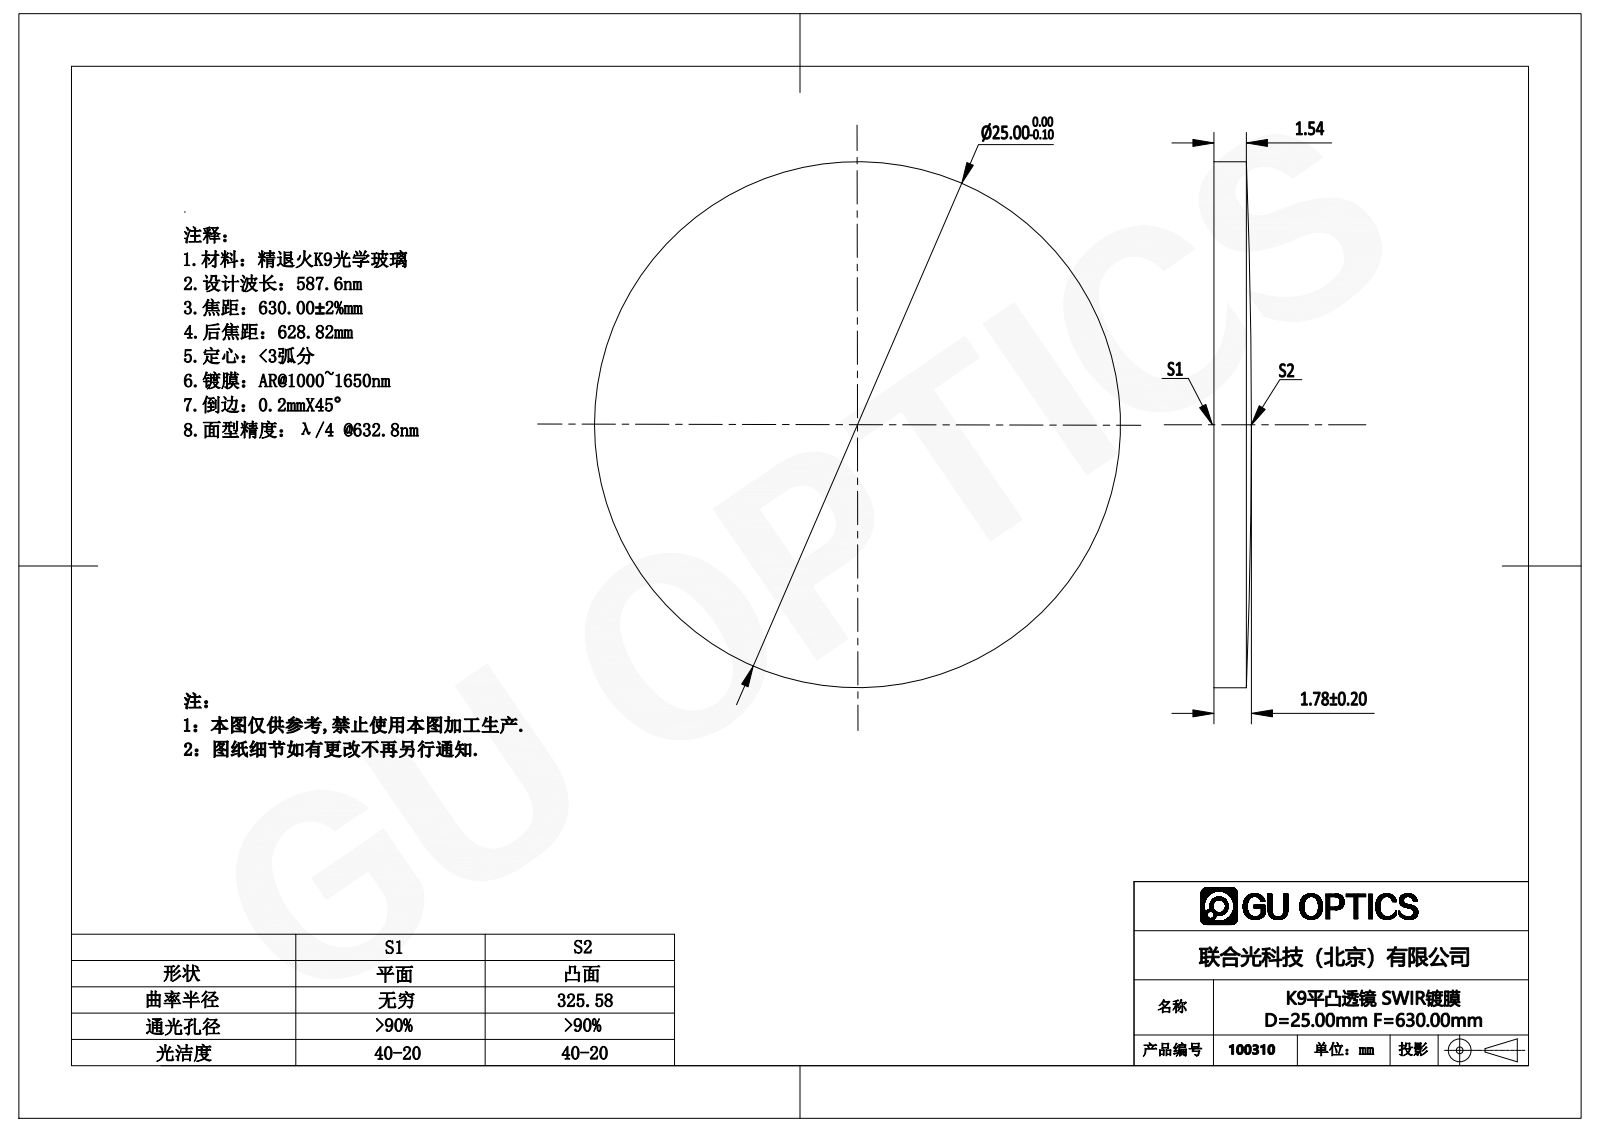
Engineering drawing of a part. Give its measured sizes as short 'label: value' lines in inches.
name: 100138
written by: SolidWorks 2016 (AUTOMOTIVE_DESIGN)
unit: in
bodies: 1 solid, 5 faces (1 planar, 2 cylindrical, 2 other)
size: 0.984 × 0.984 × 0.07
volume: 0.05 in³; area: 1.71 in²
bosses: 1× ⌀0.984
